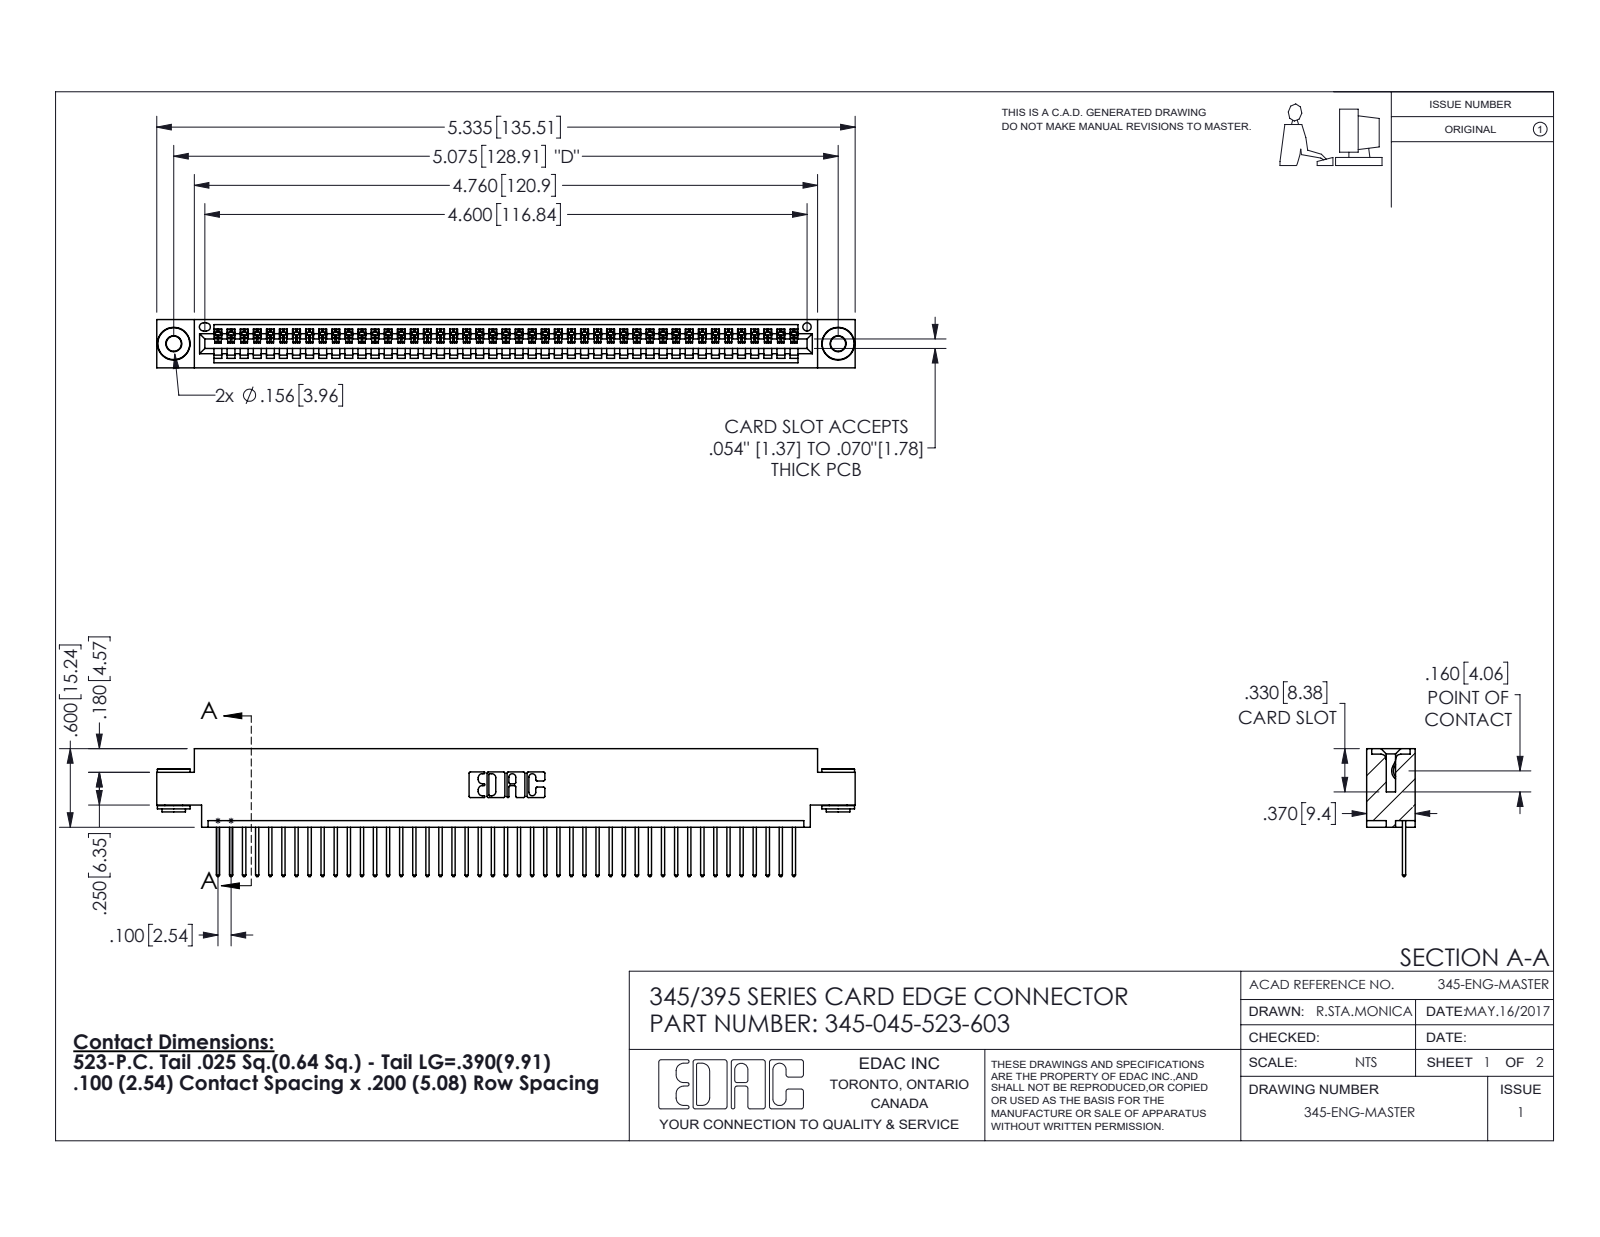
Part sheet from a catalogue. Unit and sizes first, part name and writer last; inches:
Units: inches
Overall size (bounding box): 5.335 × 0.977 × 0.37
Round holes (diameter × count): ⌀0.116 ×2, ⌀0.156 ×2, ⌀0.064 ×1
Round bosses / shafts (diameter × count): ⌀0.25 ×2, ⌀0.18 ×2, ⌀0.136 ×2
Partial cylindrical surfaces — rounded edges, fillets, slot ends (radius × count): R0.006 ×90, R0.01 ×90, R0.01 ×22, R0.007 ×6, R0.031 ×6, R0.026 ×3, R0.031 ×2, R0.04 ×2
Main face-to-face distances: 0.072, 0.298, 0.37, 0.2, 0.098, 0.272, 0.025, 0.225, 0.175, 0.149
Hole centre spacings: 0.27, 4.839, 5.075
Volume: 0.78 in³ · Surface area: 27 in²
Bodies: 48 solids, 2778 faces (1894 planar, 876 cylindrical, 8 other)
Part name (STEP PRODUCT): 345-250-002_345-250-002-102; 345-045-523-603; 345-292-001_345-293-123; 345 Part_0.170 Offset - 0.156 Dia-TH
STEP written by: SolidWorks 2016 (CONFIG_CONTROL_DESIGN)
